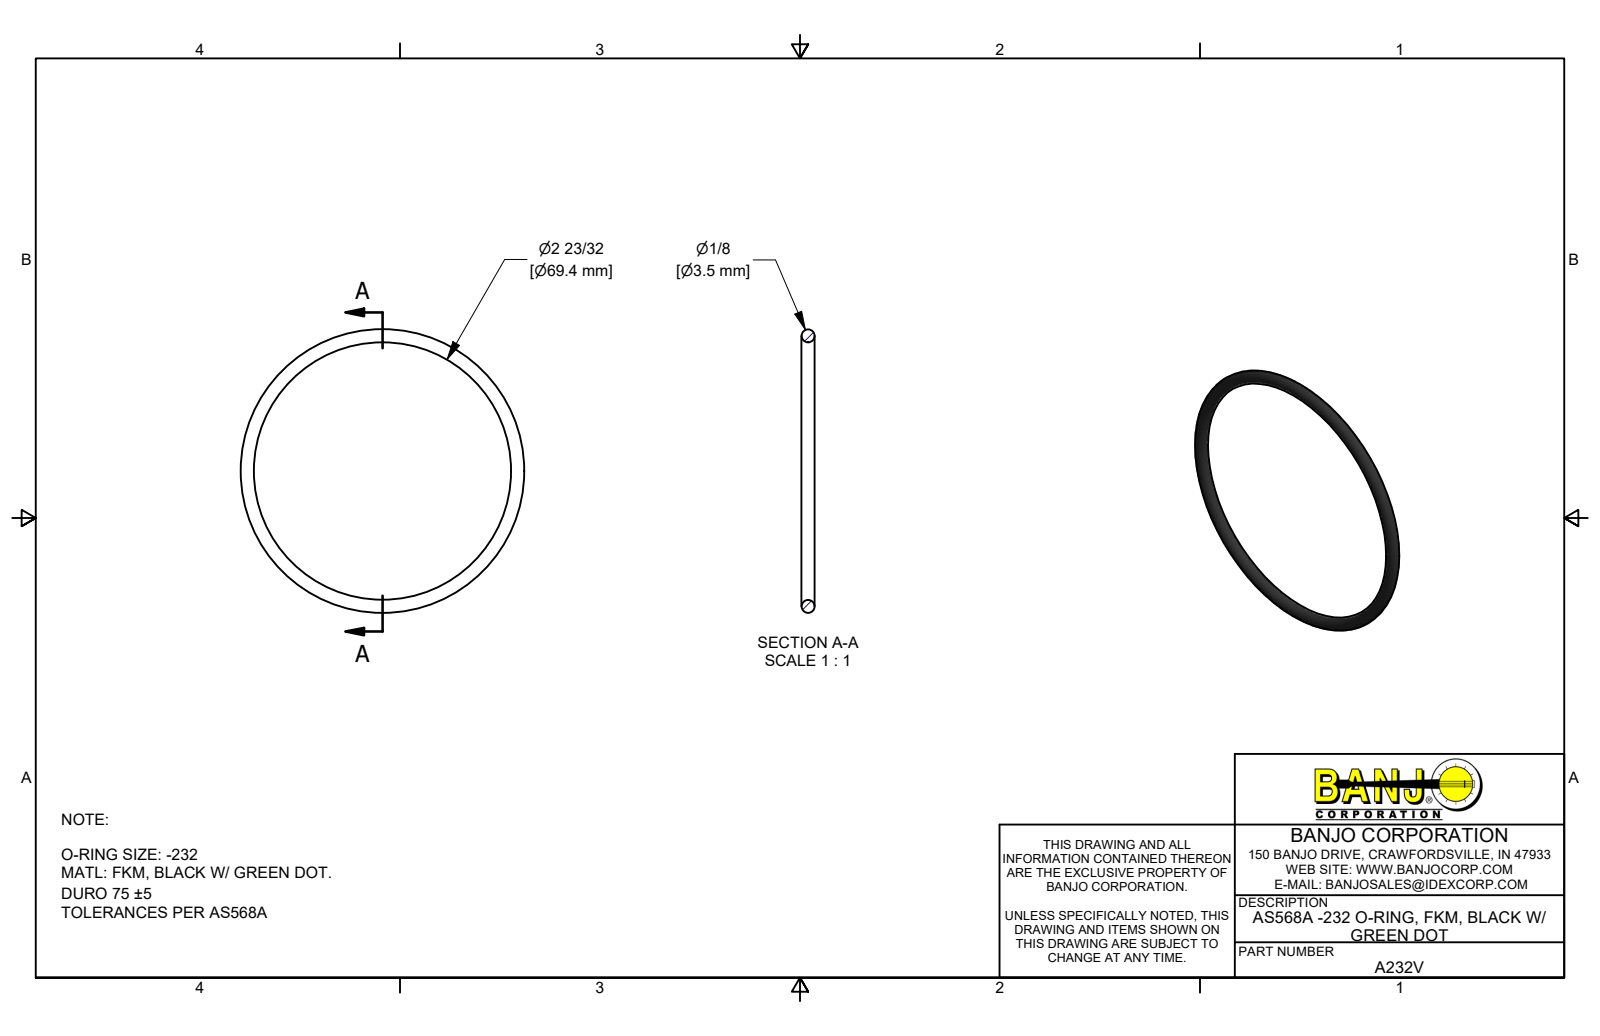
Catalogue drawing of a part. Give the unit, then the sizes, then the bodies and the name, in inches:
Units: inches
Overall size (bounding box): 3.012 × 3.012 × 0.139
Volume: 0.137 in³ · Surface area: 3.941 in²
Bodies: 1 solid, 1 faces (0 planar, 0 cylindrical, 1 other)
Part name (STEP PRODUCT): A232V
STEP written by: Autodesk Inventor 2019 (AUTOMOTIVE_DESIGN)
